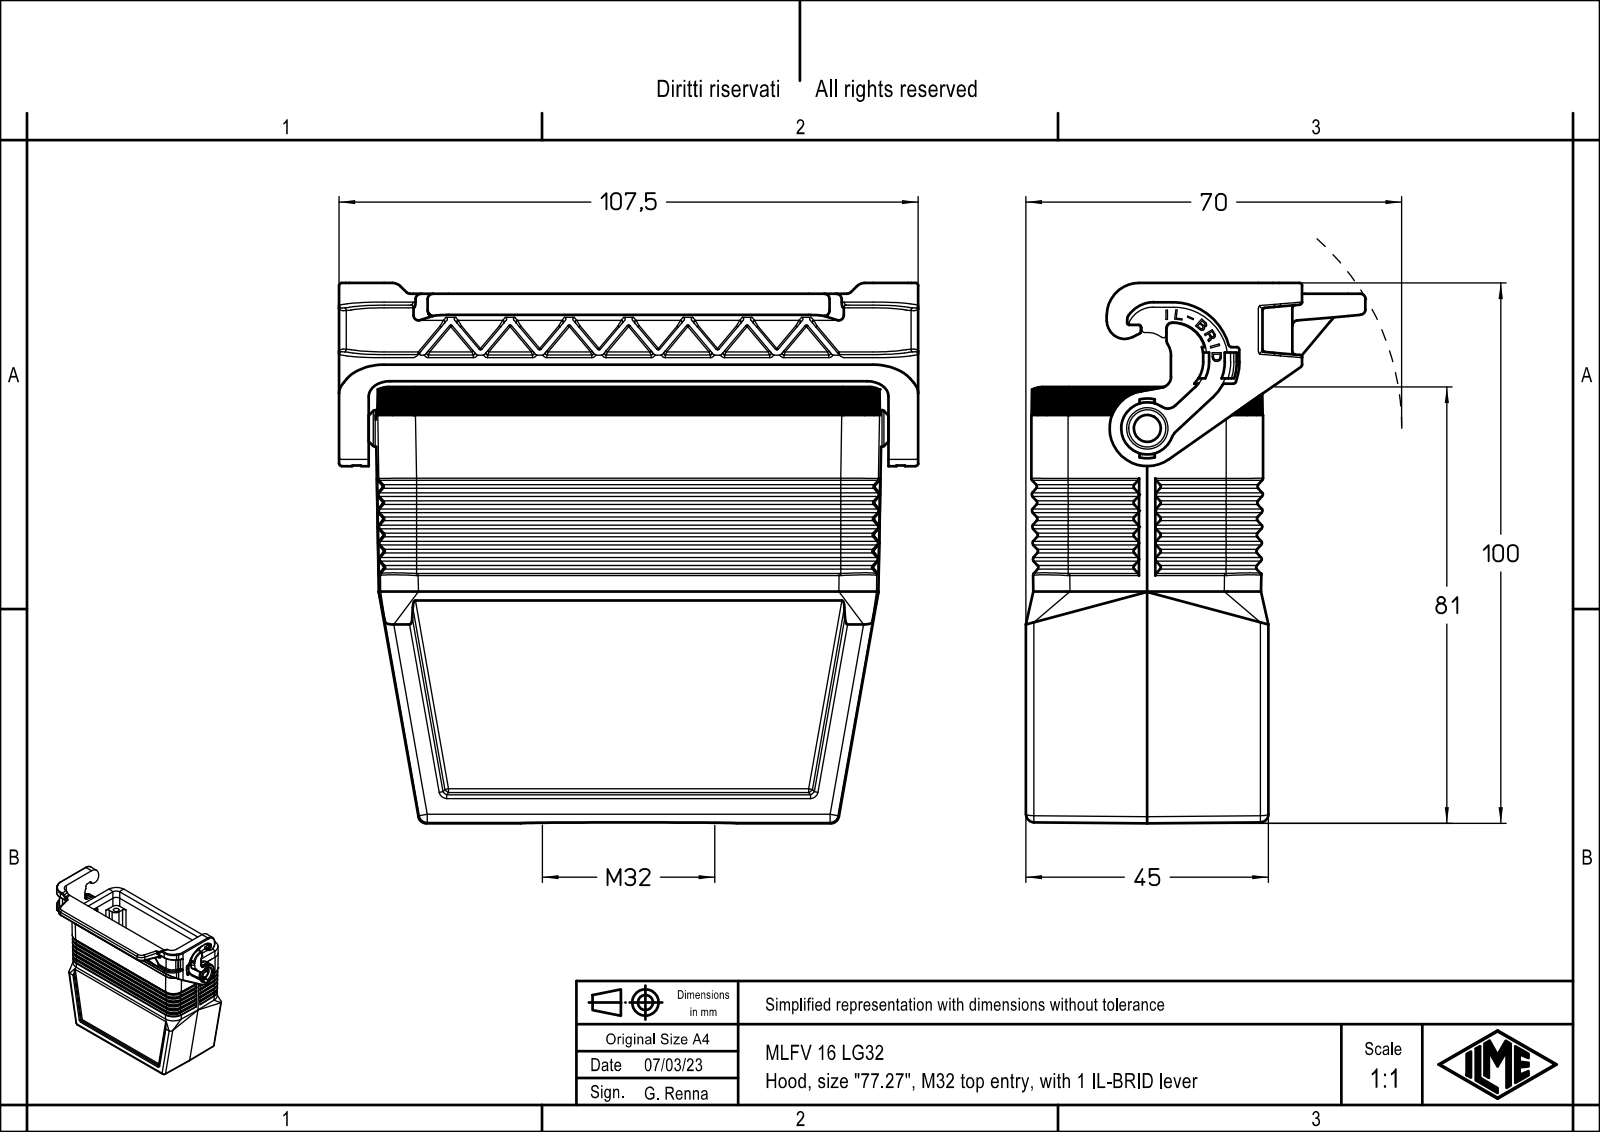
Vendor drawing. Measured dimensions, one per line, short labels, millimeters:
name: MLFV 16 LG40; MLFV 16 LG32
written by: Creo Elements/Direct Modeling 20.1B 02-Apr-2019 (C) Parametric Technology GmbH (AUTOMOTIVE_DESIGN)
unit: mm
bodies: 1 solid, 1349 faces (783 planar, 366 cylindrical, 200 other)
size: 107.5 × 100.25 × 63
volume: 109 445 mm³; area: 58 592 mm²
holes: 4× ⌀3, 4× ⌀3.5, 1× ⌀3.25, 1× ⌀5.4, 1× ⌀7.7, 1× ⌀32.5
bosses: 1× ⌀6.9, 1× ⌀6.8, 1× ⌀5.2, 1× ⌀3.2
rounds: 77× R0.5, 27× R0.1, 23× R1.5, 15× R0.2, 15× R1, 14× R7, 13× R0.33, 12× R0.55
face distances: 3.75, 39.25, 35.5, 43, 2, 7, 46.25, 3.25, 42.5, 1
hole spacings: 41.03, 27, 77.5, 82.07
